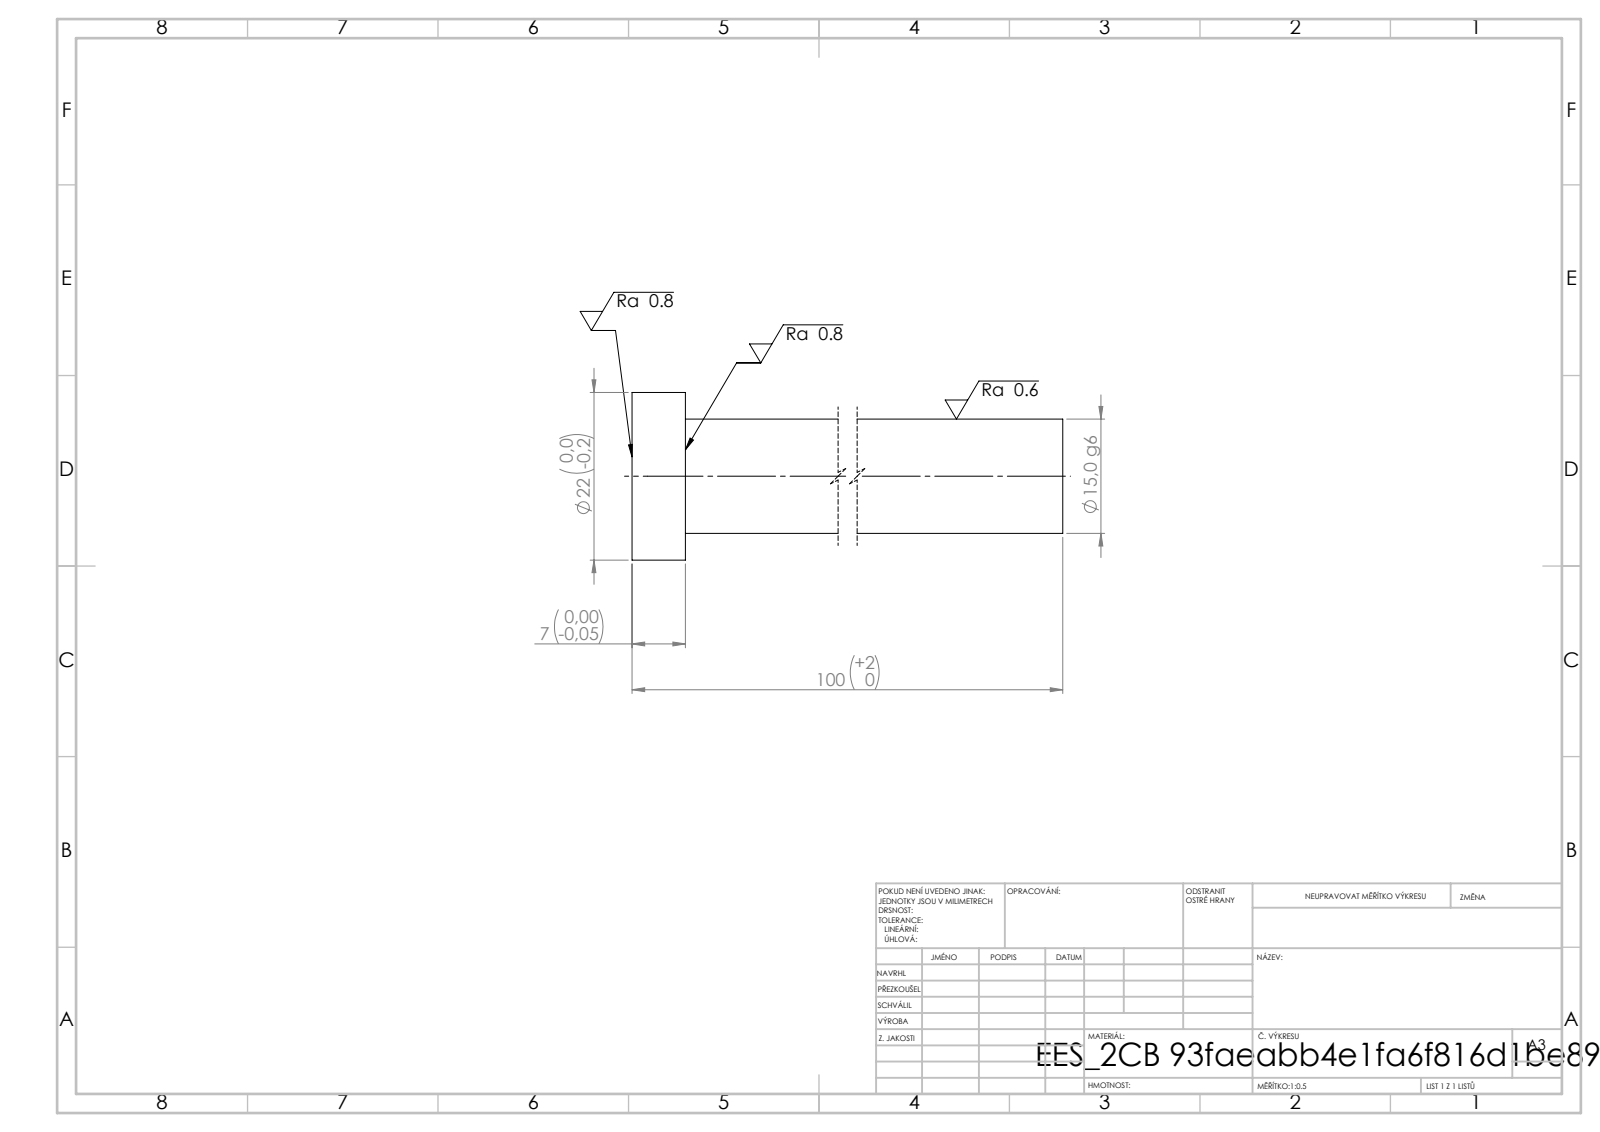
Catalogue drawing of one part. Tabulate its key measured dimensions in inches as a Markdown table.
| quantity | value |
| --- | --- |
| STEP written by | SolidWorks 2019 (CONFIG_CONTROL_DESIGN) |
| units | inches |
| bodies | 1 solid, 7 faces (3 planar, 4 cylindrical, 0 other) |
| overall size | 3.937 × 0.866 × 0.866 |
| volume | 1.165 in³ |
| surface area | 8.722 in² |
| round bosses / shafts (diameter × count) | 0.866 × 1, 0.591 × 1 |
| main face-to-face distances | 0.276, 3.937, 3.661 |
